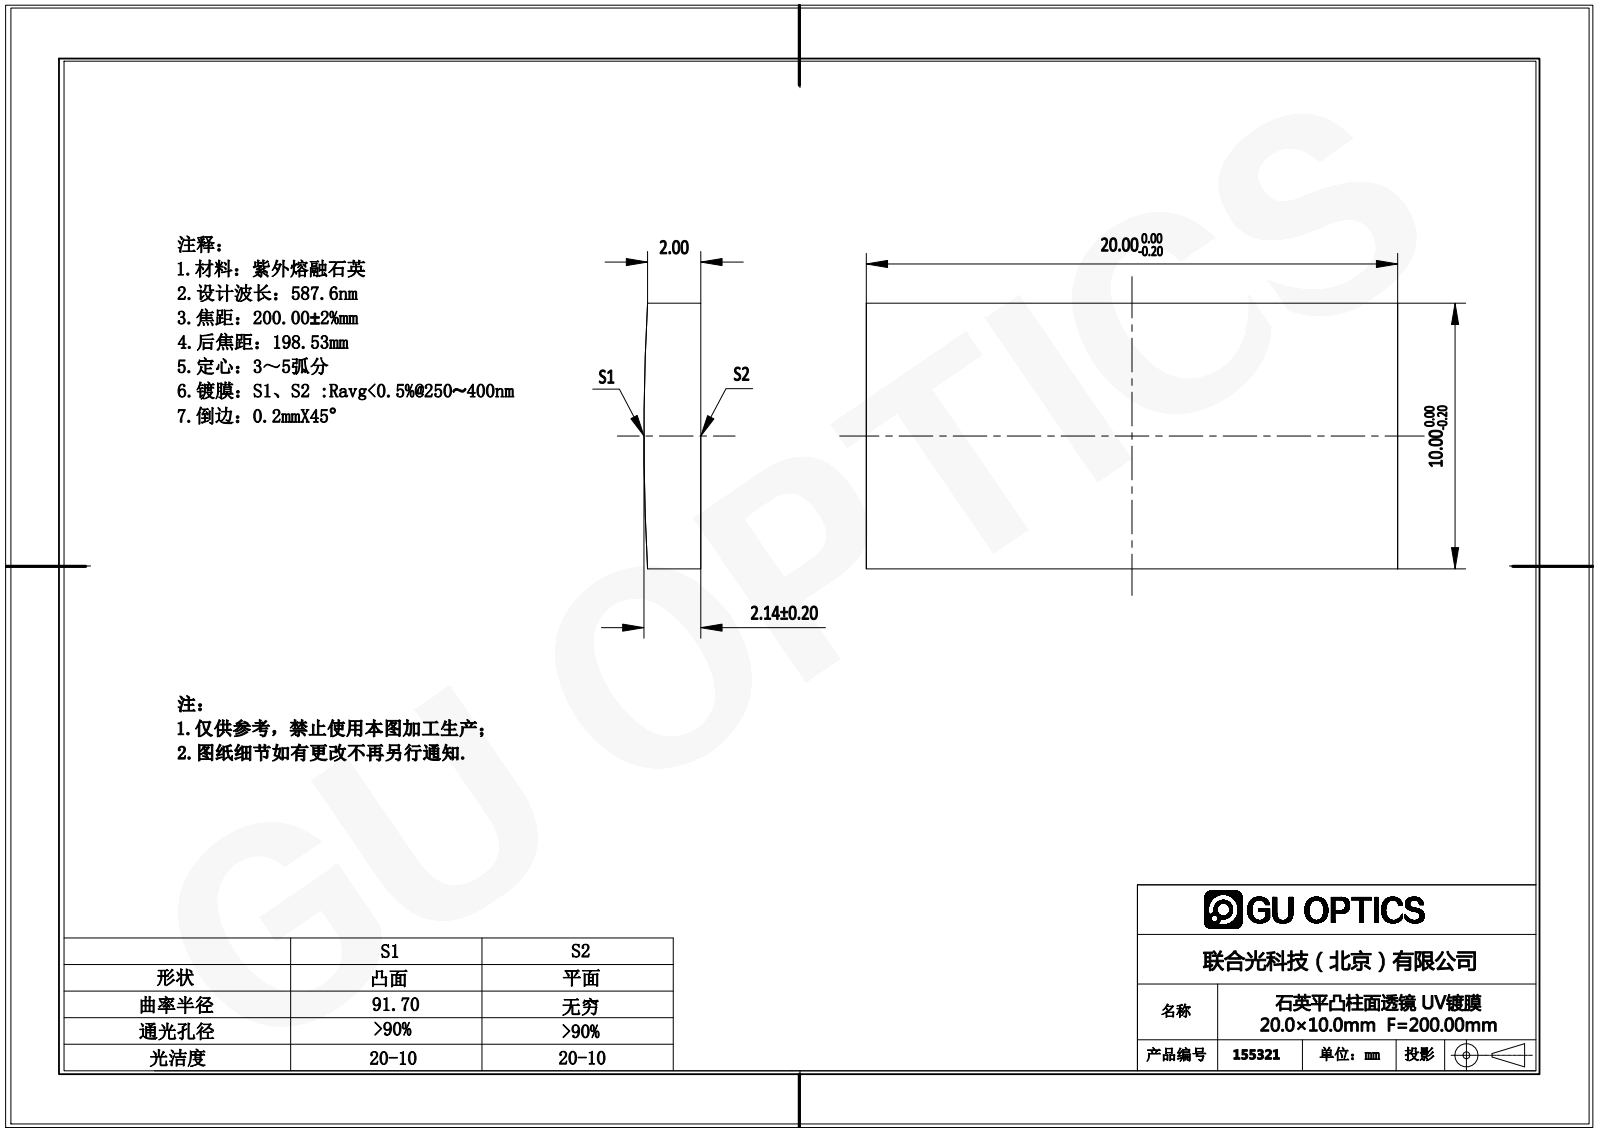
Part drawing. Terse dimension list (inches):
name: 155287
written by: SolidWorks 2016 (AUTOMOTIVE_DESIGN)
unit: in
bodies: 1 solid, 6 faces (5 planar, 1 cylindrical, 0 other)
size: 0.787 × 0.394 × 0.084
volume: 0.026 in³; area: 0.809 in²
rounds: 1× R3.61
face distances: 0.394, 0.787
